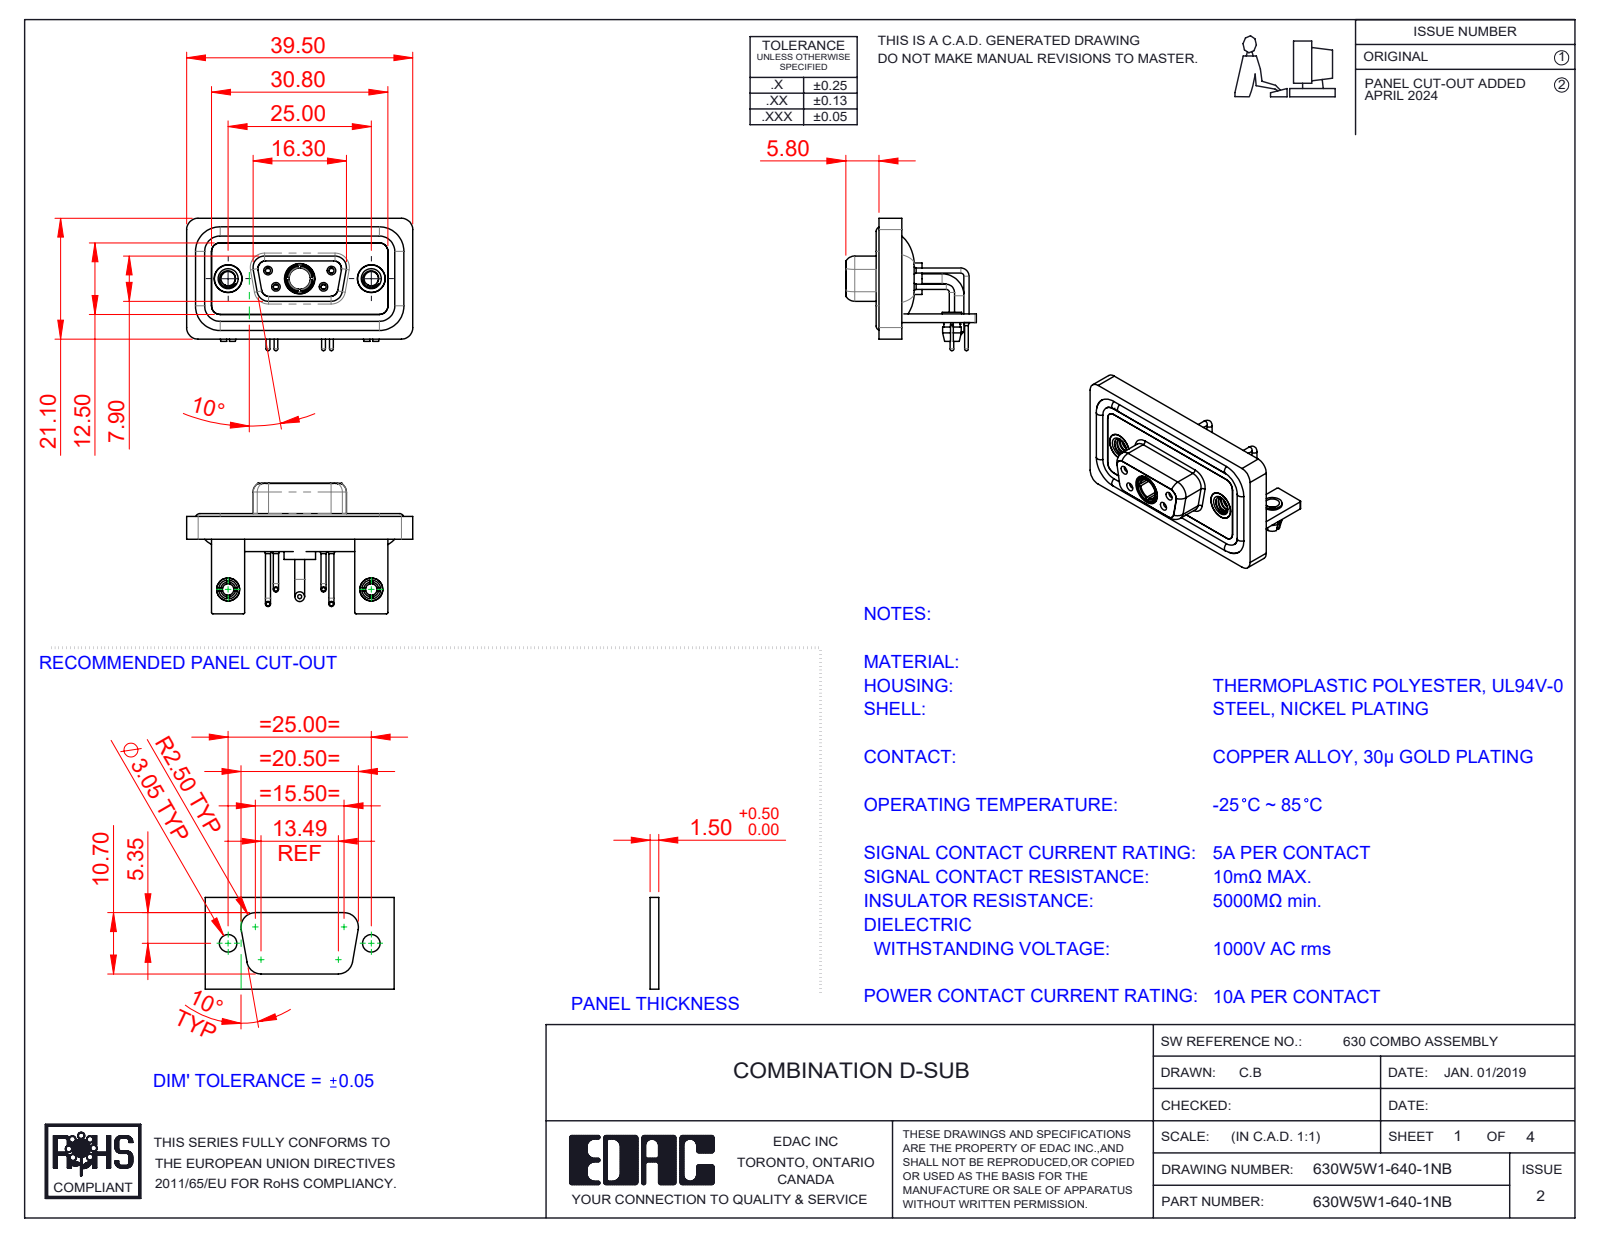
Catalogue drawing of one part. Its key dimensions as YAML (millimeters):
part_name: "630Combo Board Lock_50 Contacts; 630Combo Stabilizer Bracket_50 Contacts; 630Combo Housing_5W1; 630Combo Contact Row 1_50 Contacts (+7 more)"
step_written_by: "SolidWorks 2023 (CONFIG_CONTROL_DESIGN)"
units: millimeters
bodies: {solids: 17, faces: 810, planar: 262, cylindrical: 359, other: 189}
overall_size: [39.5, 23.12, 22.8]
volume: 5166
surface_area: 8742
round_holes:
  - {diameter: 2, count: 6}
  - {diameter: 0.9, count: 4}
  - {diameter: 1.1, count: 4}
  - {diameter: 1.5, count: 4}
  - {diameter: 2.5, count: 4}
  - {diameter: 4.85, count: 3}
  - {diameter: 1.6, count: 2}
  - {diameter: 1.7, count: 2}
  - {diameter: 3.2, count: 2}
  - {diameter: 4, count: 2}
  - {diameter: 4.05, count: 2}
  - {diameter: 5, count: 2}
round_bosses_or_shafts:
  - {diameter: 1.6, count: 6}
  - {diameter: 0.9, count: 4}
  - {diameter: 0.65, count: 4}
  - {diameter: 4.95, count: 2}
  - {diameter: 4.8, count: 2}
  - {diameter: 4, count: 2}
  - {diameter: 3.4, count: 2}
  - {diameter: 3.3, count: 2}
partial_cylinders:
  - {radius: 2, count: 19}
  - {radius: 1.5, count: 18}
  - {radius: 0.25, count: 16}
  - {radius: 1.35, count: 8}
  - {radius: 1.6, count: 8}
  - {radius: 0.5, count: 5}
  - {radius: 0.6, count: 4}
  - {radius: 0.65, count: 4}
face_to_face_distances: [0.4, 2.9, 1.5, 1.8, 1.1, 3.7, 1.6, 0.8, 2.5, 3.1]
hole_center_spacings: [3.16, 5.72, 7.1, 12.5, 18.1, 25, 4.39, 4.4]
